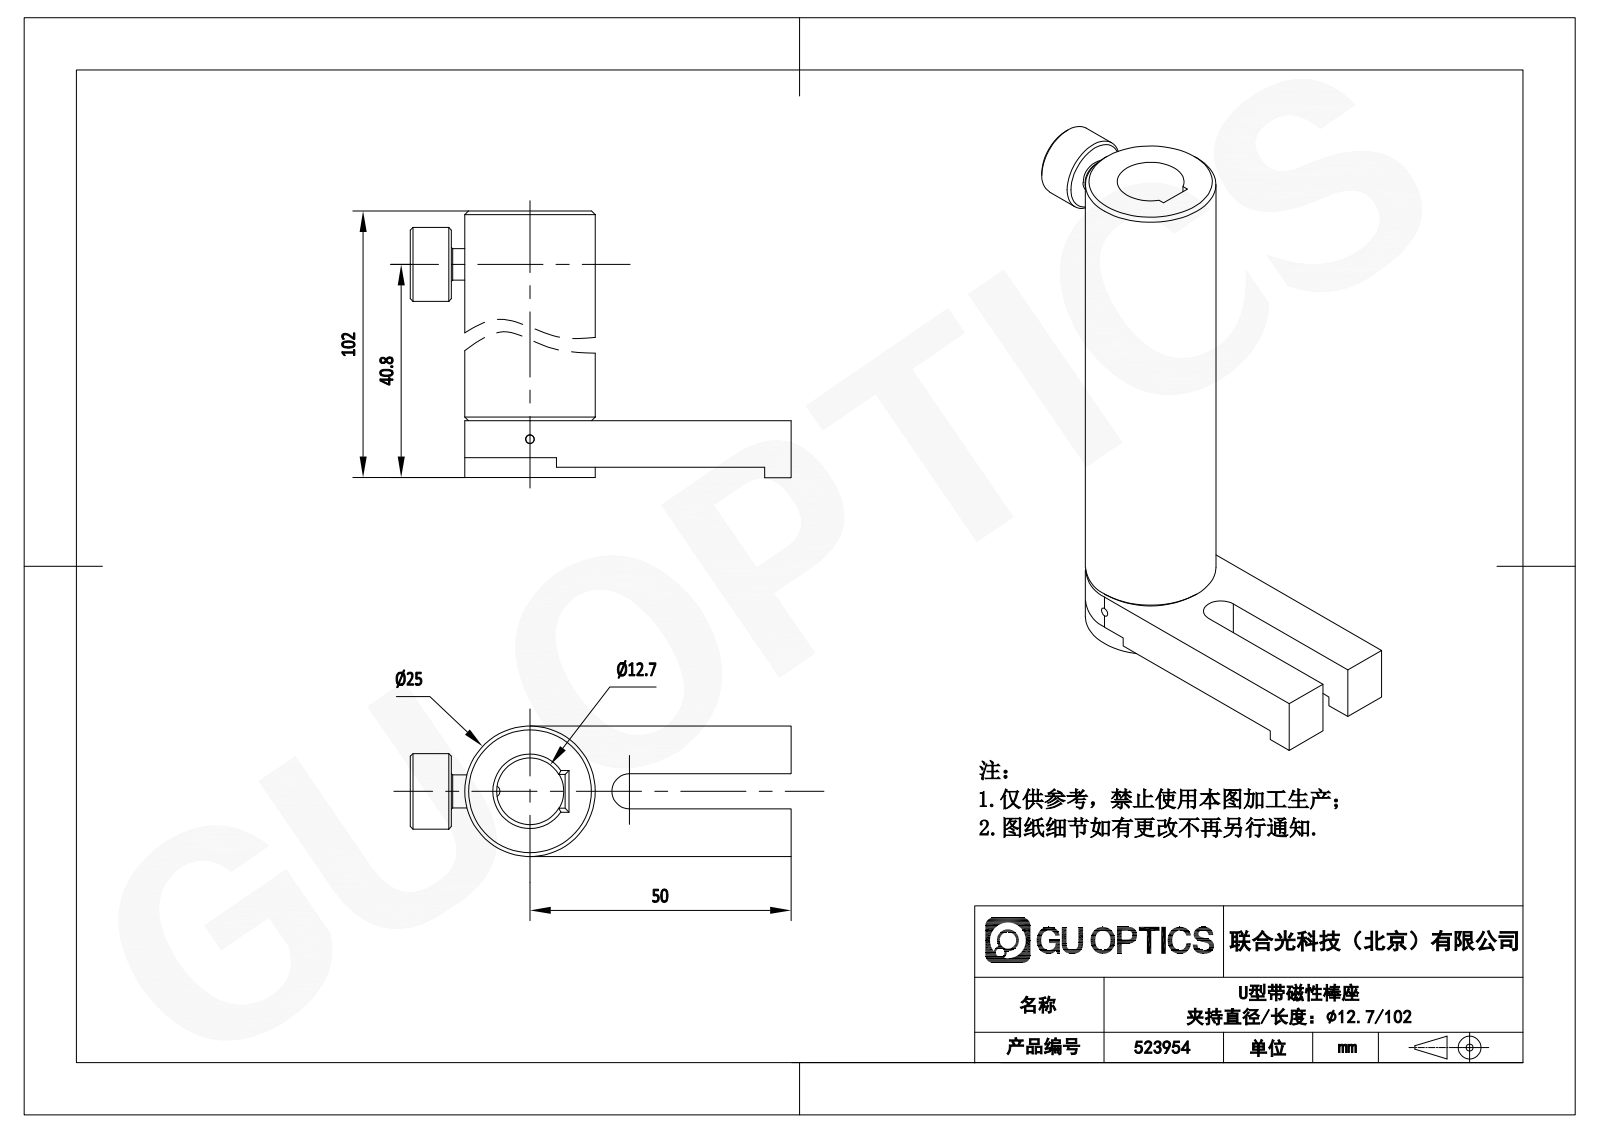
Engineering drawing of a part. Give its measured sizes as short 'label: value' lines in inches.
name: 523954
written by: SolidWorks 2016 (CONFIG_CONTROL_DESIGN)
unit: in
bodies: 8 solids, 128 faces (38 planar, 50 cylindrical, 40 other)
size: 4.053 × 2.87 × 0.984
volume: 2.78 in³; area: 30.86 in²
holes: 3× ⌀0.19, 1× ⌀0.063, 1× ⌀0.067, 1× ⌀0.07, 1× ⌀0.503, 1× ⌀0.51, 1× ⌀0.791
bosses: 3× ⌀0.187, 1× ⌀0.984, 1× ⌀0.789, 1× ⌀0.7, 1× ⌀0.68, 1× ⌀0.556, 1× ⌀0.236, 1× ⌀0.118
rounds: 1× R0.133, 1× R0.51
face distances: 0.35, 0.359, 0.625, 0.984, 0.072, 0.278, 0.078, 0.15, 0.428, 4.016
hole spacings: 0.65, 0.375, 0.375
